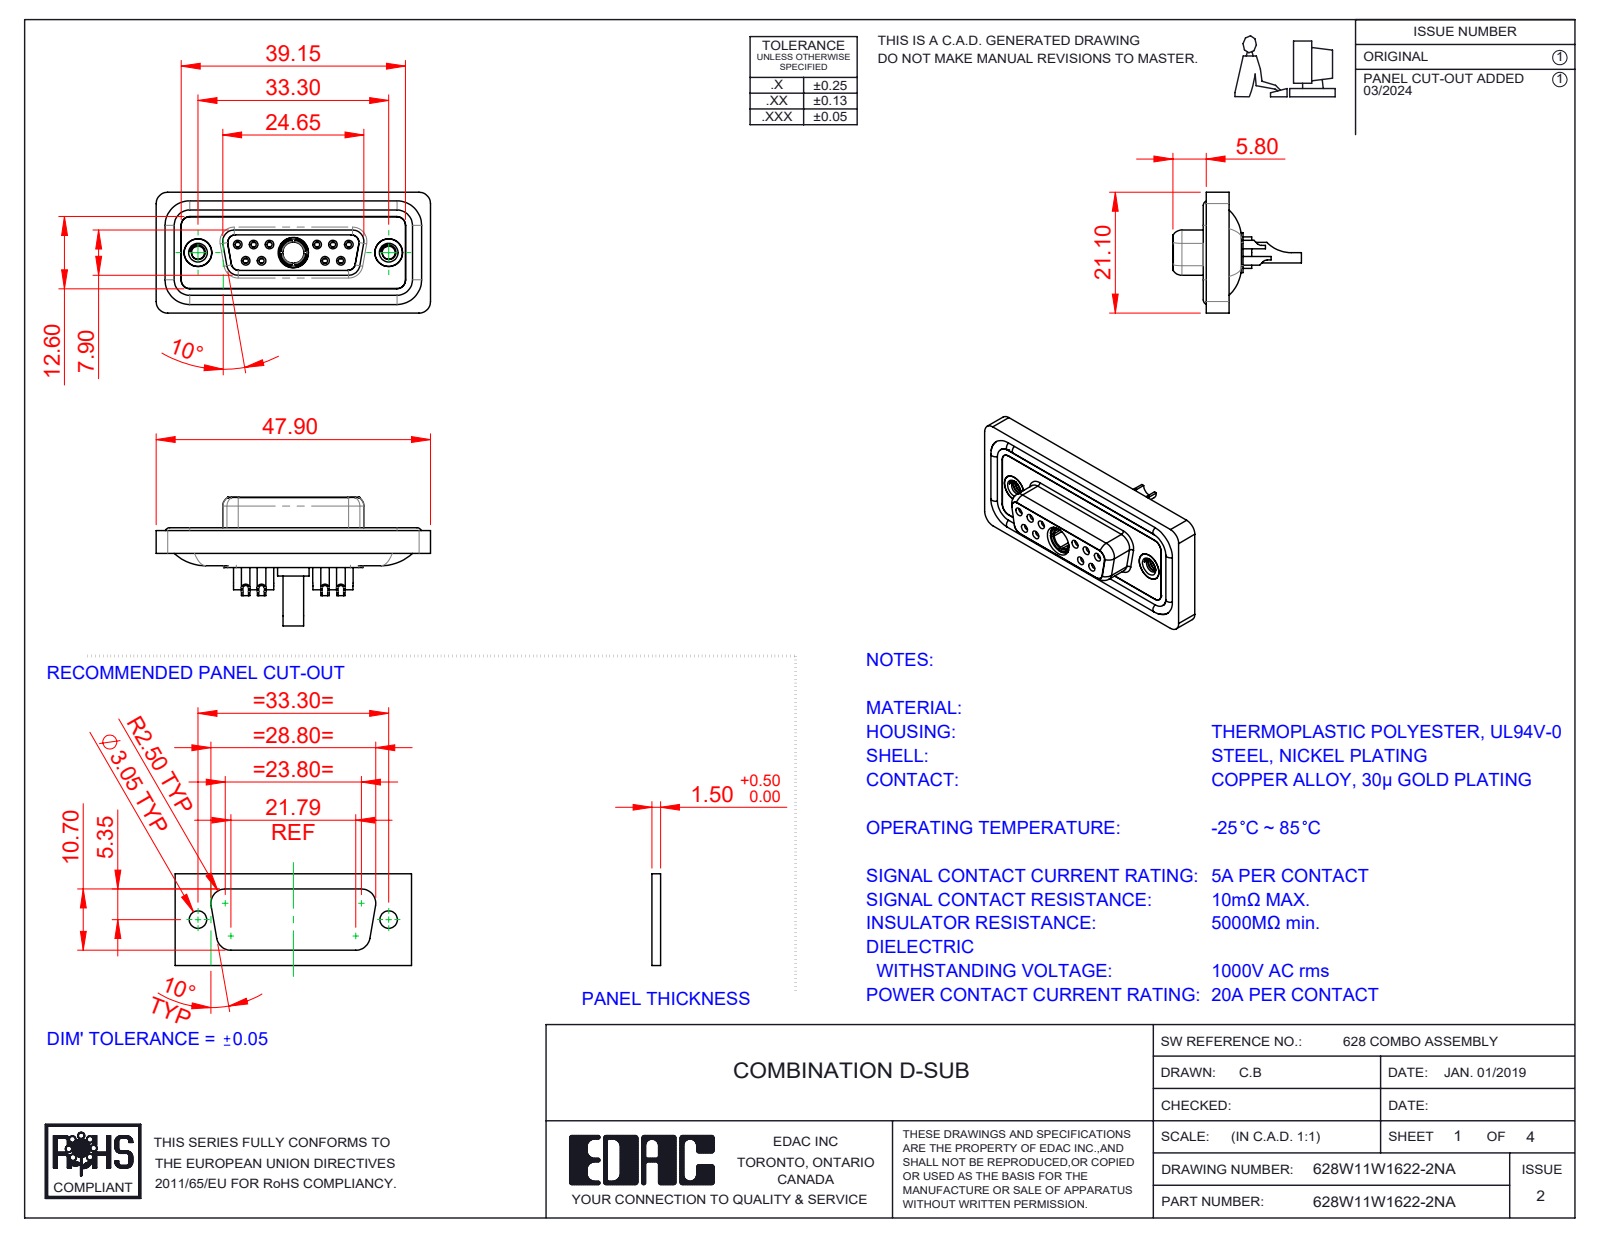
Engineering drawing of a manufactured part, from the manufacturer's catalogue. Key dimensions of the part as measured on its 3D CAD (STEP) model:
Part name (STEP PRODUCT): 628Combo Threaded Rivet_A; 628Combo Housing_11W1; 628Combo Shell Front_15 Contacts; 628Combo Contact Row 1_22 (+5 more)
STEP written by: SolidWorks 2023 (CONFIG_CONTROL_DESIGN)
Units: millimetres
Bodies: 19 solids, 1014 faces (307 planar, 426 cylindrical, 281 other)
Overall size (bounding box): 47.9 × 22.45 × 21.1
Volume: 6 159 mm³ · Surface area: 10 212 mm²
Round holes (diameter × count): ⌀0.9 ×10, ⌀1 ×10, ⌀1.1 ×10, ⌀1.5 ×10, ⌀2 ×10, ⌀1.7 ×6, ⌀1.6 ×4, ⌀4.85 ×3, ⌀2.26 ×2, ⌀4 ×2, ⌀4.05 ×2, ⌀5 ×2
Round bosses / shafts (diameter × count): ⌀2.2 ×10, ⌀1.6 ×10, ⌀4.95 ×2, ⌀4.8 ×2, ⌀5.5 ×1, ⌀5.2 ×1, ⌀4.96 ×1, ⌀4.75 ×1
Partial cylindrical surfaces — rounded edges, fillets, slot ends (radius × count): R1.5 ×22, R2 ×20, R1.35 ×12, R1.6 ×8, R1 ×6, R0.25 ×4, R0.5 ×4, R0.6 ×4
Main face-to-face distances: 0.4, 1.6, 1.8, 2.9, 0.5, 1.1, 5.65, 7.45, 6.6, 7.05
Hole centre spacings: 3.16, 2.77, 13.85, 11.08, 16.62, 5.03, 5.04, 5.54
